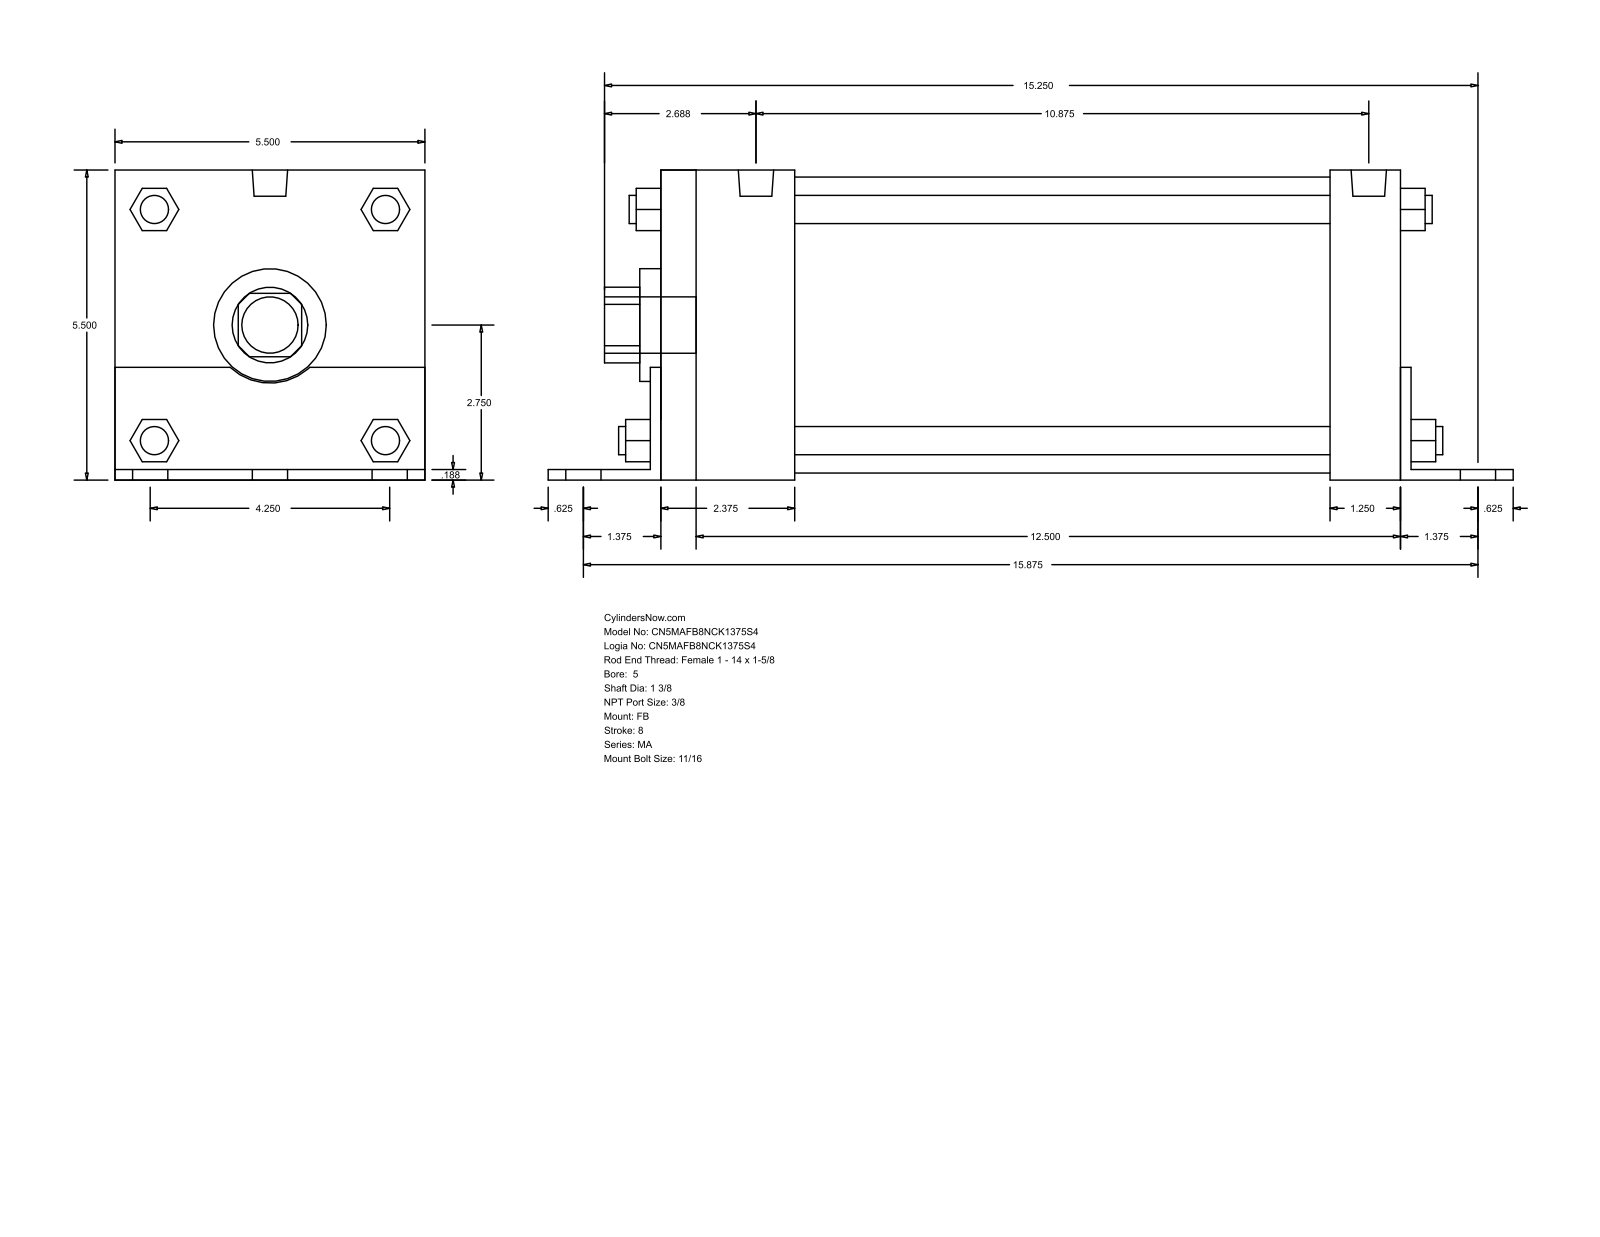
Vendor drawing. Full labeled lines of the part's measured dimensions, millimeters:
Part name (STEP PRODUCT): MA_FB__0500_1.375
STEP written by: GSSL Pune (CONFIG_CONTROL_DESIGN)
Units: millimetres
Bodies: 0 solids, 140 faces (105 planar, 35 cylindrical, 0 other)
Overall size (bounding box): 434.98 × 139.75 × 139.7
Round holes (diameter × count): ⌀34.92 ×1, ⌀50.8 ×1, ⌀133.35 ×1
Round bosses / shafts (diameter × count): ⌀17.46 ×6, ⌀12.7 ×4, ⌀11.11 ×4, ⌀15.93 ×2, ⌀25.4 ×1
Partial cylindrical surfaces — rounded edges, fillets, slot ends (radius × count): R17.06 ×1, R26.16 ×1
Main face-to-face distances: 139.7, 4.76, 139.75, 4.71, 134.99, 333.37, 4.77, 338.14, 338.13, 342.9
